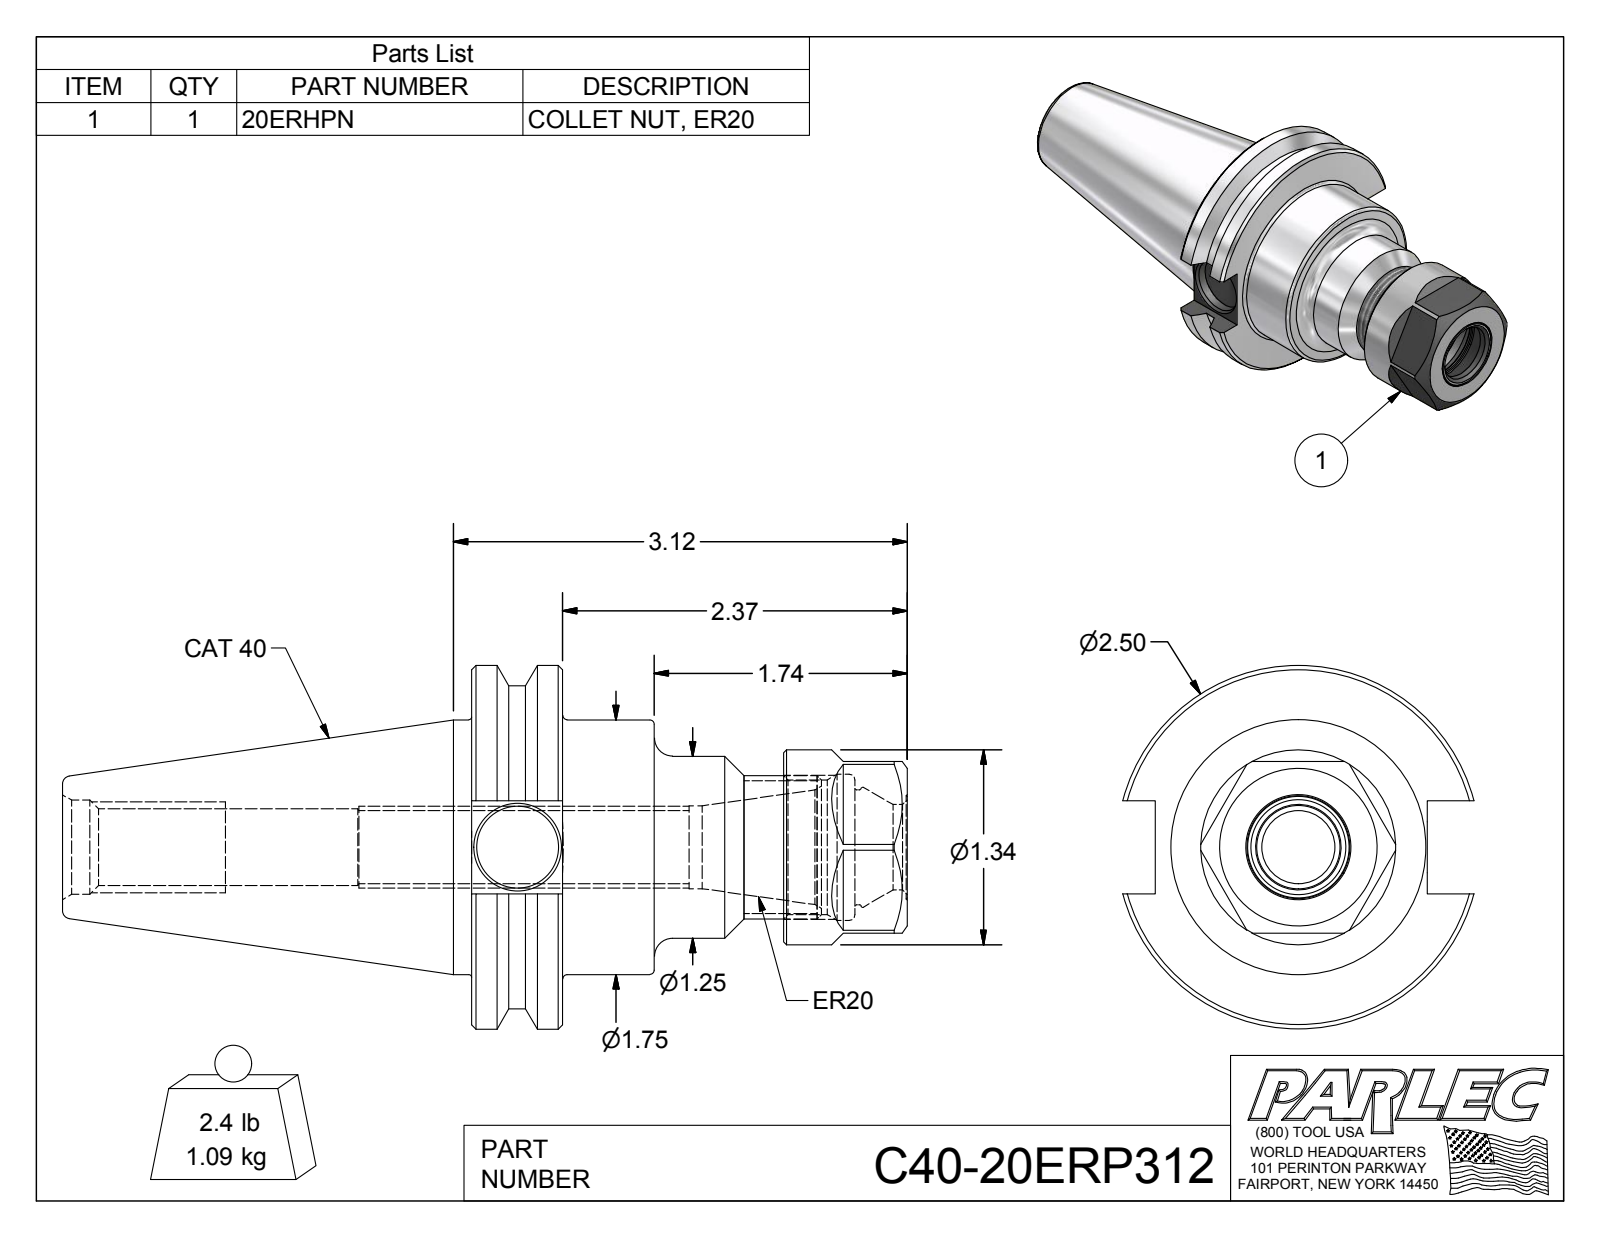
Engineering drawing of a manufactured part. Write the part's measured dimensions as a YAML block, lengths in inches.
part_name: "C40-20ERP312; C40-20ER3-1; 20ERHPN"
step_written_by: "Autodesk Inventor 2018 (AUTOMOTIVE_DESIGN)"
units: inches
bodies: {solids: 2, faces: 85, planar: 29, cylindrical: 21, other: 35}
overall_size: [5.808, 2.5, 2.417]
volume: 8.929
surface_area: 48.54
round_holes:
  - {diameter: 0.315, count: 1}
  - {diameter: 0.399, count: 1}
  - {diameter: 0.502, count: 1}
  - {diameter: 0.527, count: 1}
  - {diameter: 0.57, count: 1}
  - {diameter: 0.587, count: 1}
  - {diameter: 0.648, count: 1}
  - {diameter: 0.79, count: 1}
  - {diameter: 0.926, count: 1}
  - {diameter: 1.005, count: 1}
round_bosses_or_shafts:
  - {diameter: 2.5, count: 1}
  - {diameter: 2.219, count: 1}
  - {diameter: 1.75, count: 1}
  - {diameter: 1.34, count: 1}
  - {diameter: 1.25, count: 1}
  - {diameter: 0.984, count: 1}
face_to_face_distances: [0.625, 1.18, 2.145, 1.52, 2.995, 2.37, 0.85, 0.27, 0.91, 1.255]
